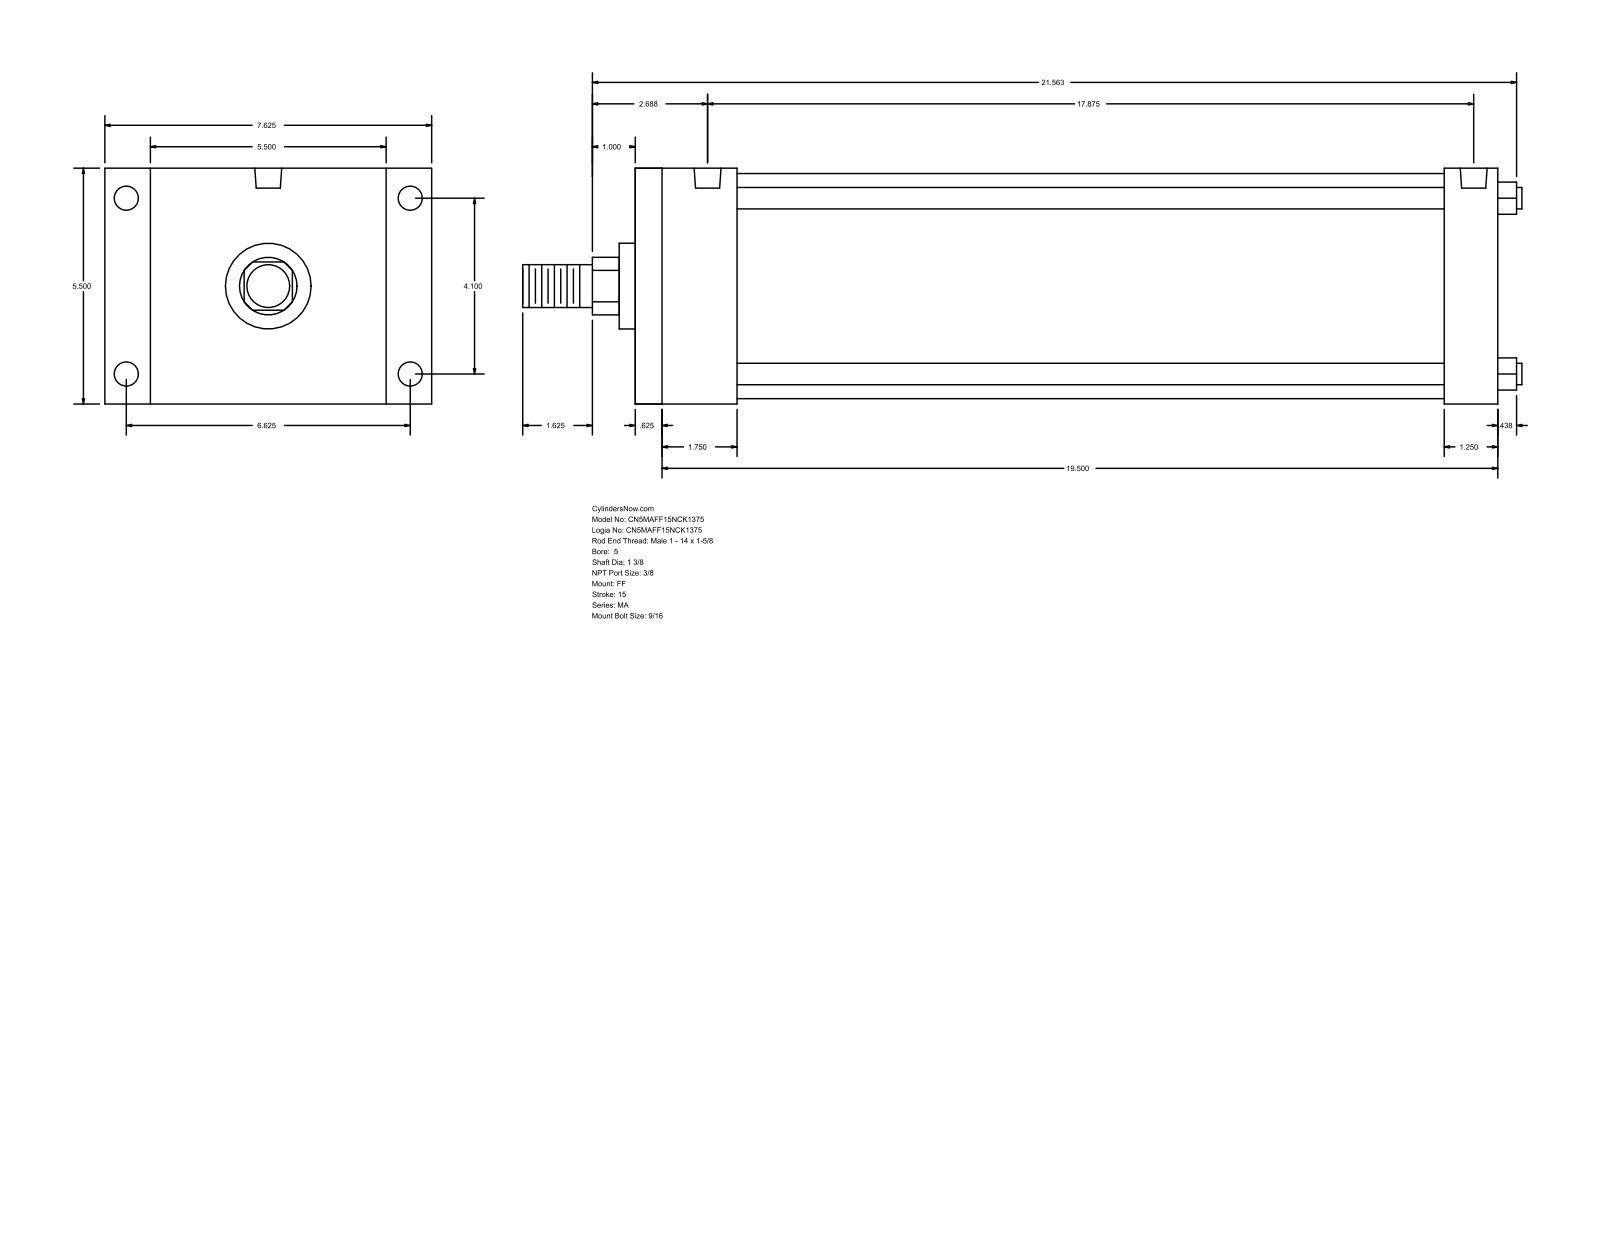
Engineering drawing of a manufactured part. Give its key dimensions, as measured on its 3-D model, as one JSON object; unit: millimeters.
{"part_name": "MA_FF__0500_1.375", "step_written_by": "GSSL Pune (CONFIG_CONTROL_DESIGN)", "units": "millimeters", "bodies": {"solids": 0, "faces": 92, "planar": 64, "cylindrical": 28, "other": 0}, "overall_size": [592.14, 193.68, 139.7], "round_holes": [[11.11, 4], [14.29, 4], [15.93, 2]], "round_bosses_or_shafts": [[12.7, 4], [133.35, 1], [50.8, 1], [34.92, 1], [25.4, 1]], "partial_cylinders_radius": [[17.06, 1]], "face_to_face_distances": [139.7, 511.18, 15.87, 495.31, 479.42, 463.55, 31.76, 60.32, 44.45, 419.1], "hole_center_spacings": [4.77, 104.14, 168.28, 197.9, 444.49, 449.26, 454.03]}
